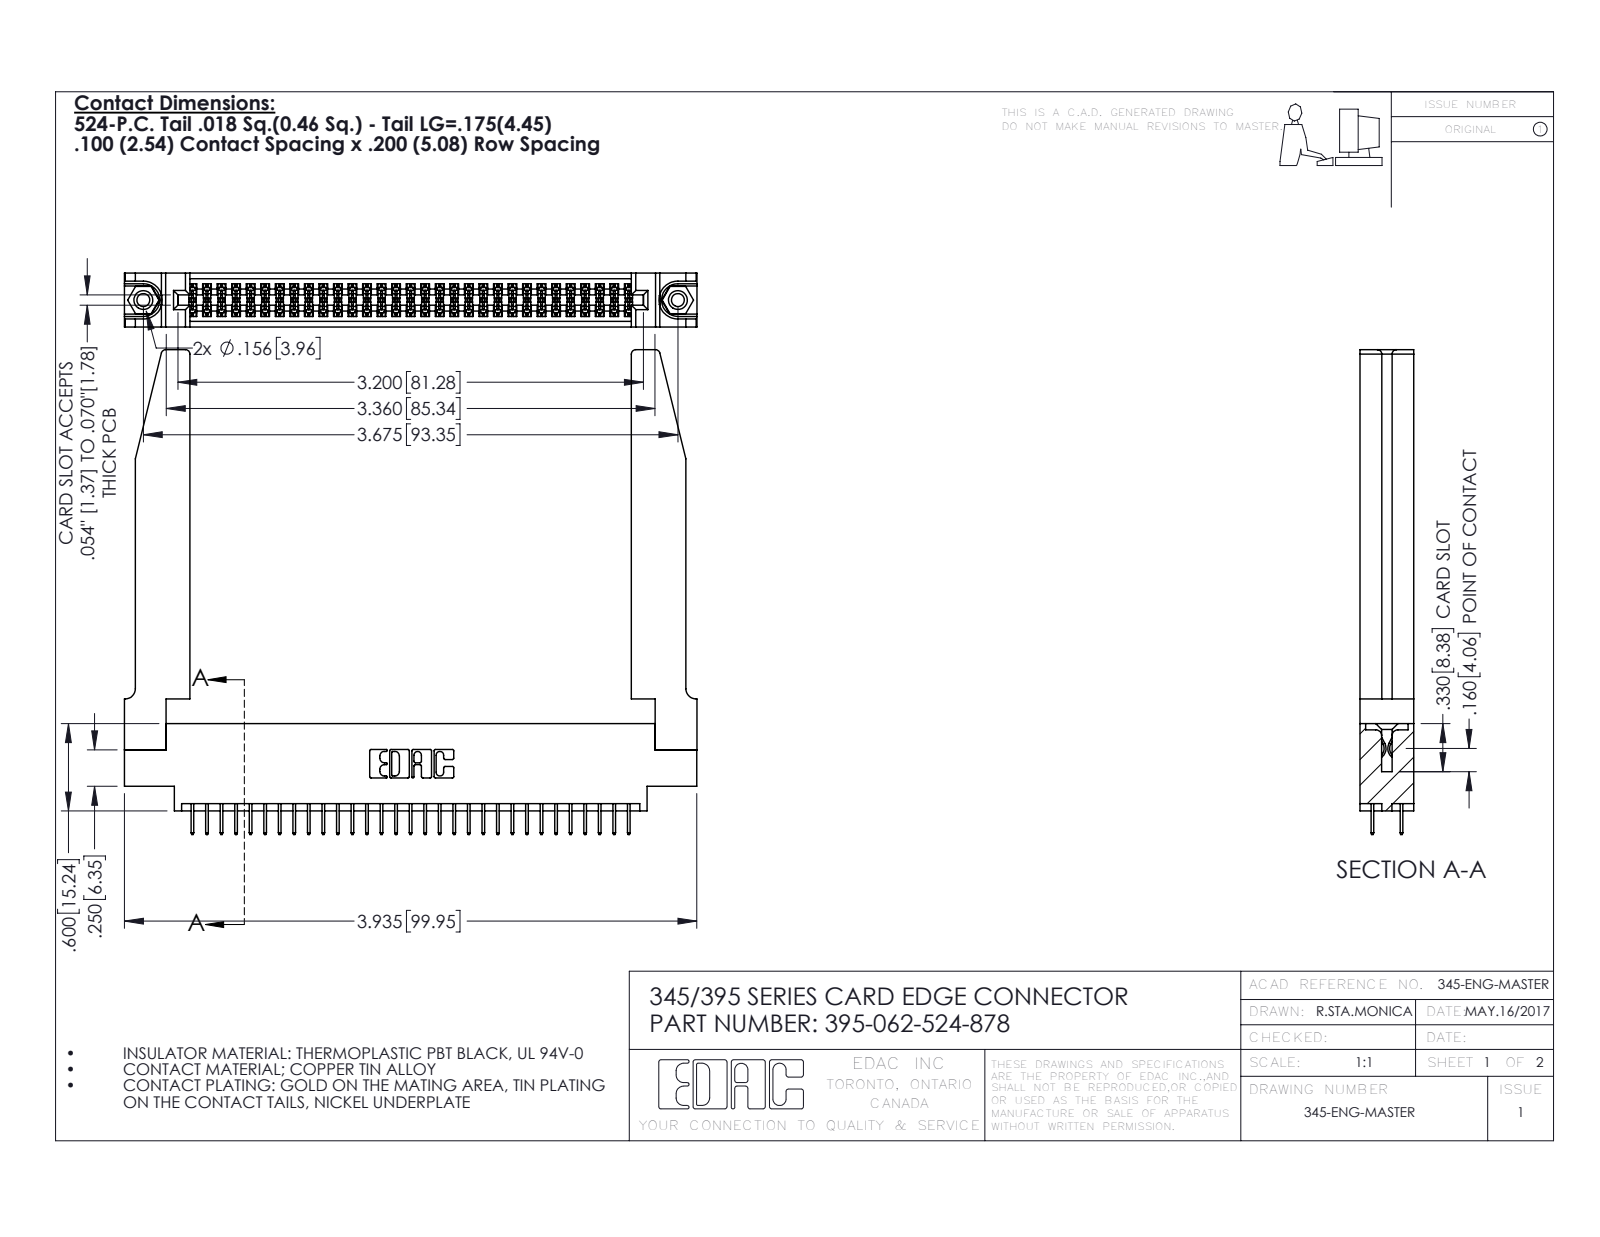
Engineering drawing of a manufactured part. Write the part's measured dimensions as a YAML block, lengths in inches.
part_name: "345-220-078_345-220-078; 345-292-001_345-293-124; 345-250-001_345-250-001-102; 395-062-524-878 (+1 more)"
step_written_by: "SolidWorks 2016 (CONFIG_CONTROL_DESIGN)"
units: inches
bodies: {solids: 67, faces: 3712, planar: 2644, cylindrical: 1016, other: 52}
overall_size: [3.936, 3.332, 0.37]
volume: 1.048
surface_area: 31.65
round_holes:
  - {diameter: 0.089, count: 2}
  - {diameter: 0.125, count: 2}
  - {diameter: 0.156, count: 2}
  - {diameter: 0.064, count: 1}
round_bosses_or_shafts:
  - {diameter: 0.155, count: 2}
partial_cylinders:
  - {radius: 0.006, count: 93}
  - {radius: 0.01, count: 22}
  - {radius: 0.03, count: 8}
  - {radius: 0.007, count: 6}
  - {radius: 0.031, count: 6}
  - {radius: 0.026, count: 3}
  - {radius: 0.014, count: 2}
  - {radius: 0.019, count: 2}
face_to_face_distances: [0.37, 0.072, 0.298, 0.098, 0.272, 0.025, 0.2, 0.225, 0.15, 0.148]
hole_center_spacings: [0.27, 3.44, 3.675]
